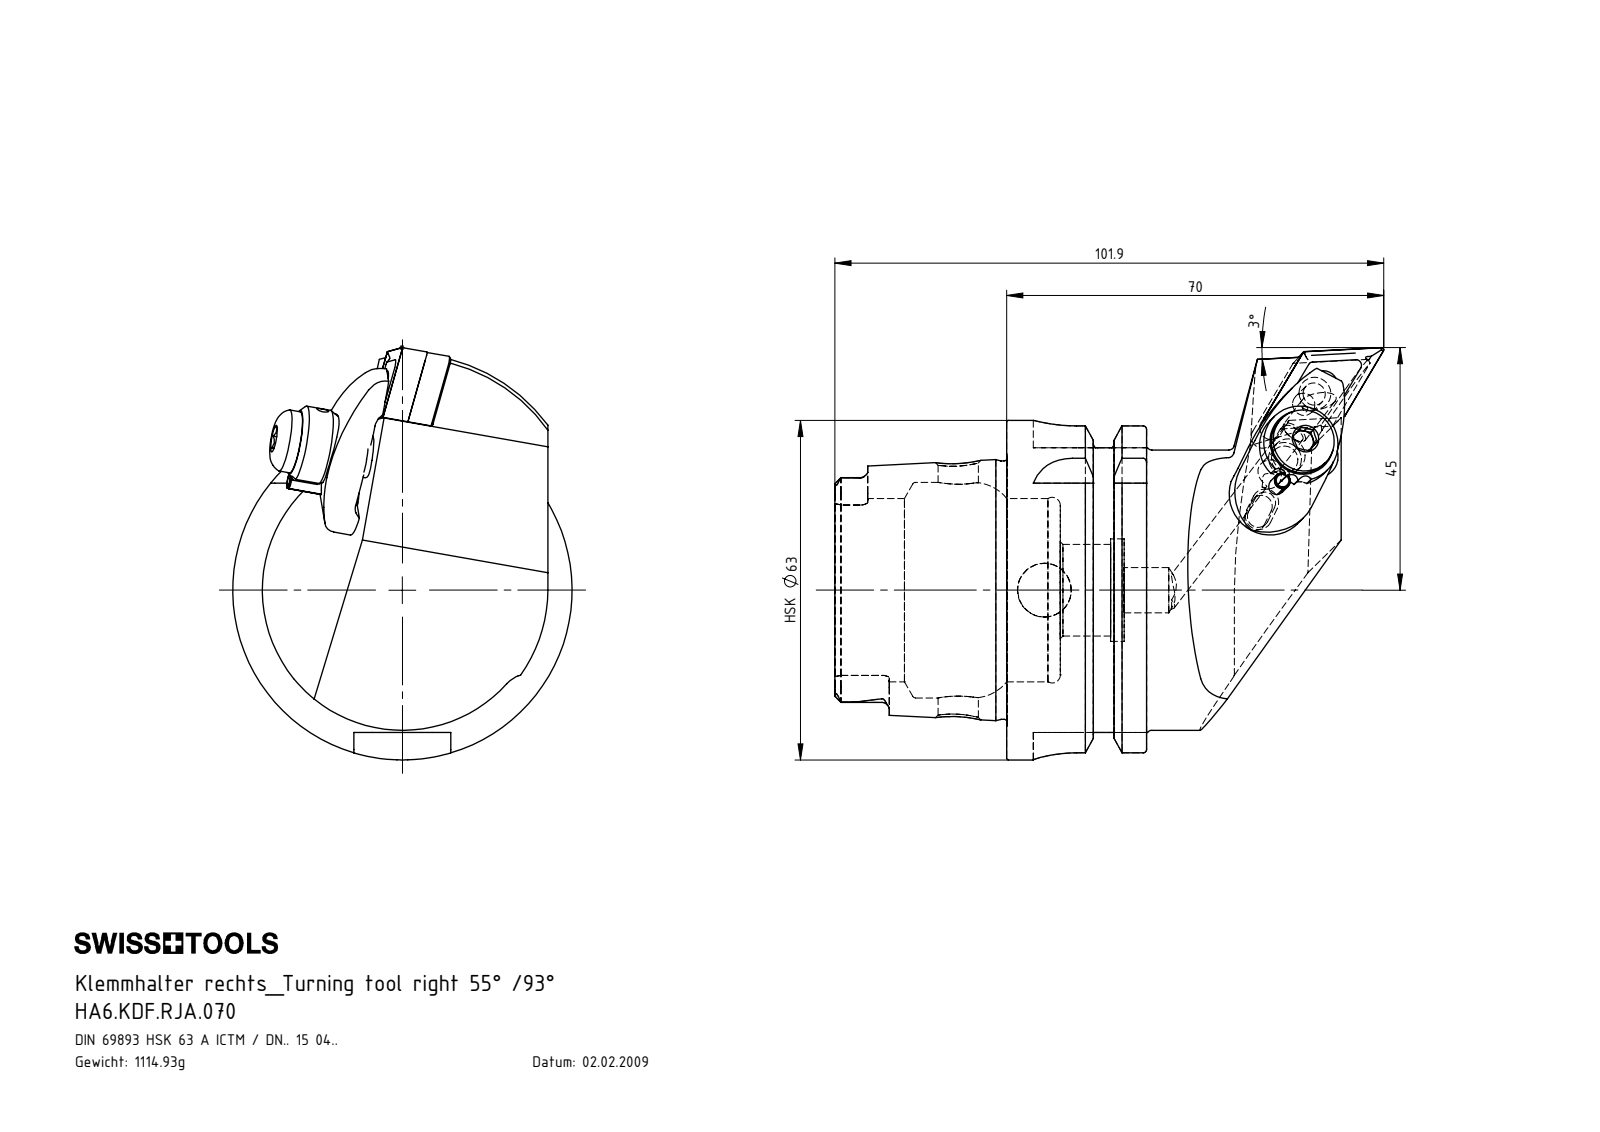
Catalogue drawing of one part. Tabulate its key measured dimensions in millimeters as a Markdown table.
| quantity | value |
| --- | --- |
| part name | KVT_MB_600_050; HA6-KDF.RJA.070_B; WCC-ER4.103.032_A; DNMG150604 (+8 more) |
| STEP written by | SolidWorks 2017 (CONFIG_CONTROL_DESIGN) |
| units | millimeters |
| bodies | 12 solids, 472 faces (127 planar, 151 cylindrical, 194 other) |
| overall size | 101.9 × 76.5 × 63 |
| volume | 141 433 mm³ |
| surface area | 34 938 mm² |
| round holes (diameter × count) | 2 × 3, 4.2 × 2, 5 × 2, 7 × 2, 2.4 × 1, 3 × 1, 4 × 1, 5.16 × 1, 6.2 × 1, 6.4 × 1, 7.5 × 1, 8.4 × 1 |
| round bosses / shafts (diameter × count) | 5 × 2, 3 × 2, 63 × 1, 54.95 × 1, 52 × 1, 47.94 × 1, 14 × 1, 11.5 × 1 |
| partial cylindrical surfaces (radius × count) | 0.39 × 6, 1.4 × 6, 0.4 × 4, 1 × 4, 8 × 4, 0.69 × 3, 0.69 × 3, 1.5 × 3 |
| main face-to-face distances | 25.95, 16, 9.95, 31.9, 41.85, 57.85, 6.05, 52.8, 3.18, 9.23 |
| hole center spacings | 23, 14.99, 8, 8.01, 8.2, 14.8, 15 |
